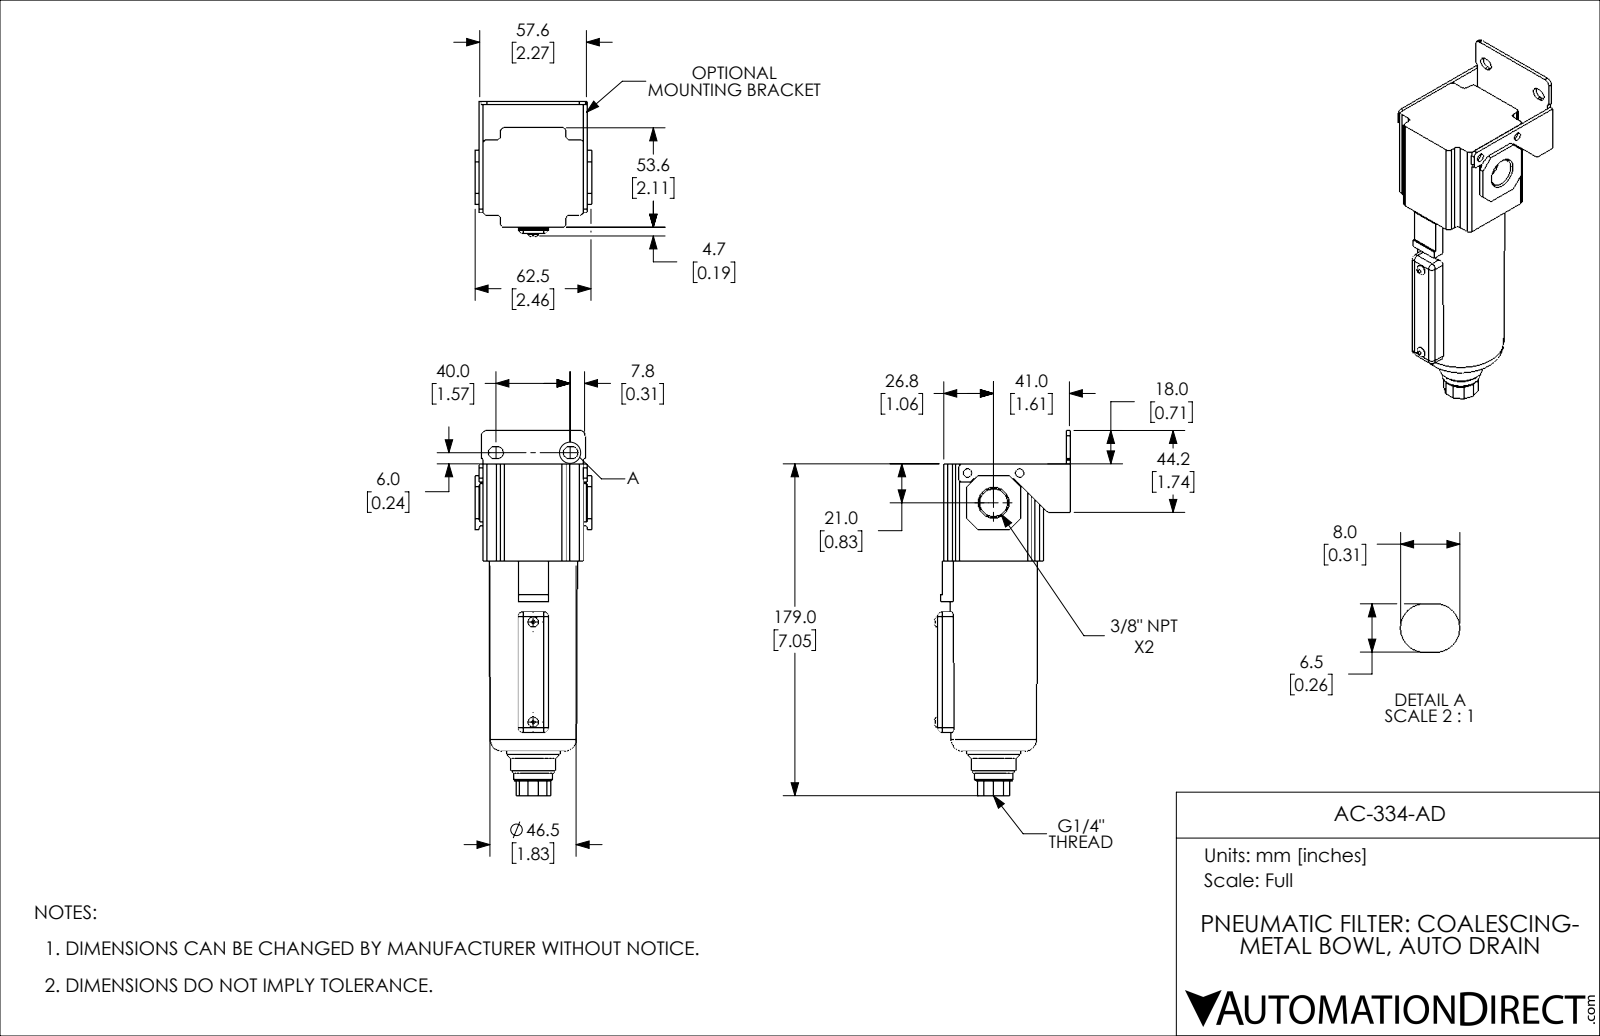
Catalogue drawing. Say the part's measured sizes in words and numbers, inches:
The part is named "AC-334-AD". Its 3-D file was written by "SolidWorks 2018 (AUTOMOTIVE_DESIGN)". It is 1 solid with 200 faces: 116 planar, 60 cylindrical and 24 other. Overall it measures 7.756 by 2.854 by 2.461 inches. Its volume is 20.38 cubic inches and its surface area 67.35 square inches. Round holes: 2 of diameter 0.177, 1 of diameter 0.451, 1 of diameter 0.589. Round bosses or shafts: 2 of diameter 0.217, 1 of diameter 1.102, 1 of diameter 0.906, 1 of diameter 0.787. Partial cylindrical surfaces (rounded edges, fillets, slot ends): 15 of radius 0.079, 8 of radius 0.098, 4 of radius 0.128, 2 of radius 0.039, 2 of radius 0.118. The main face-to-face distances are 0.079, 2.11, 2.189, 0.559, 2.669, 0.48, 2.591, 2.067, 0.258, 1.852. The hole center spacings are 0.837, 1.102.
